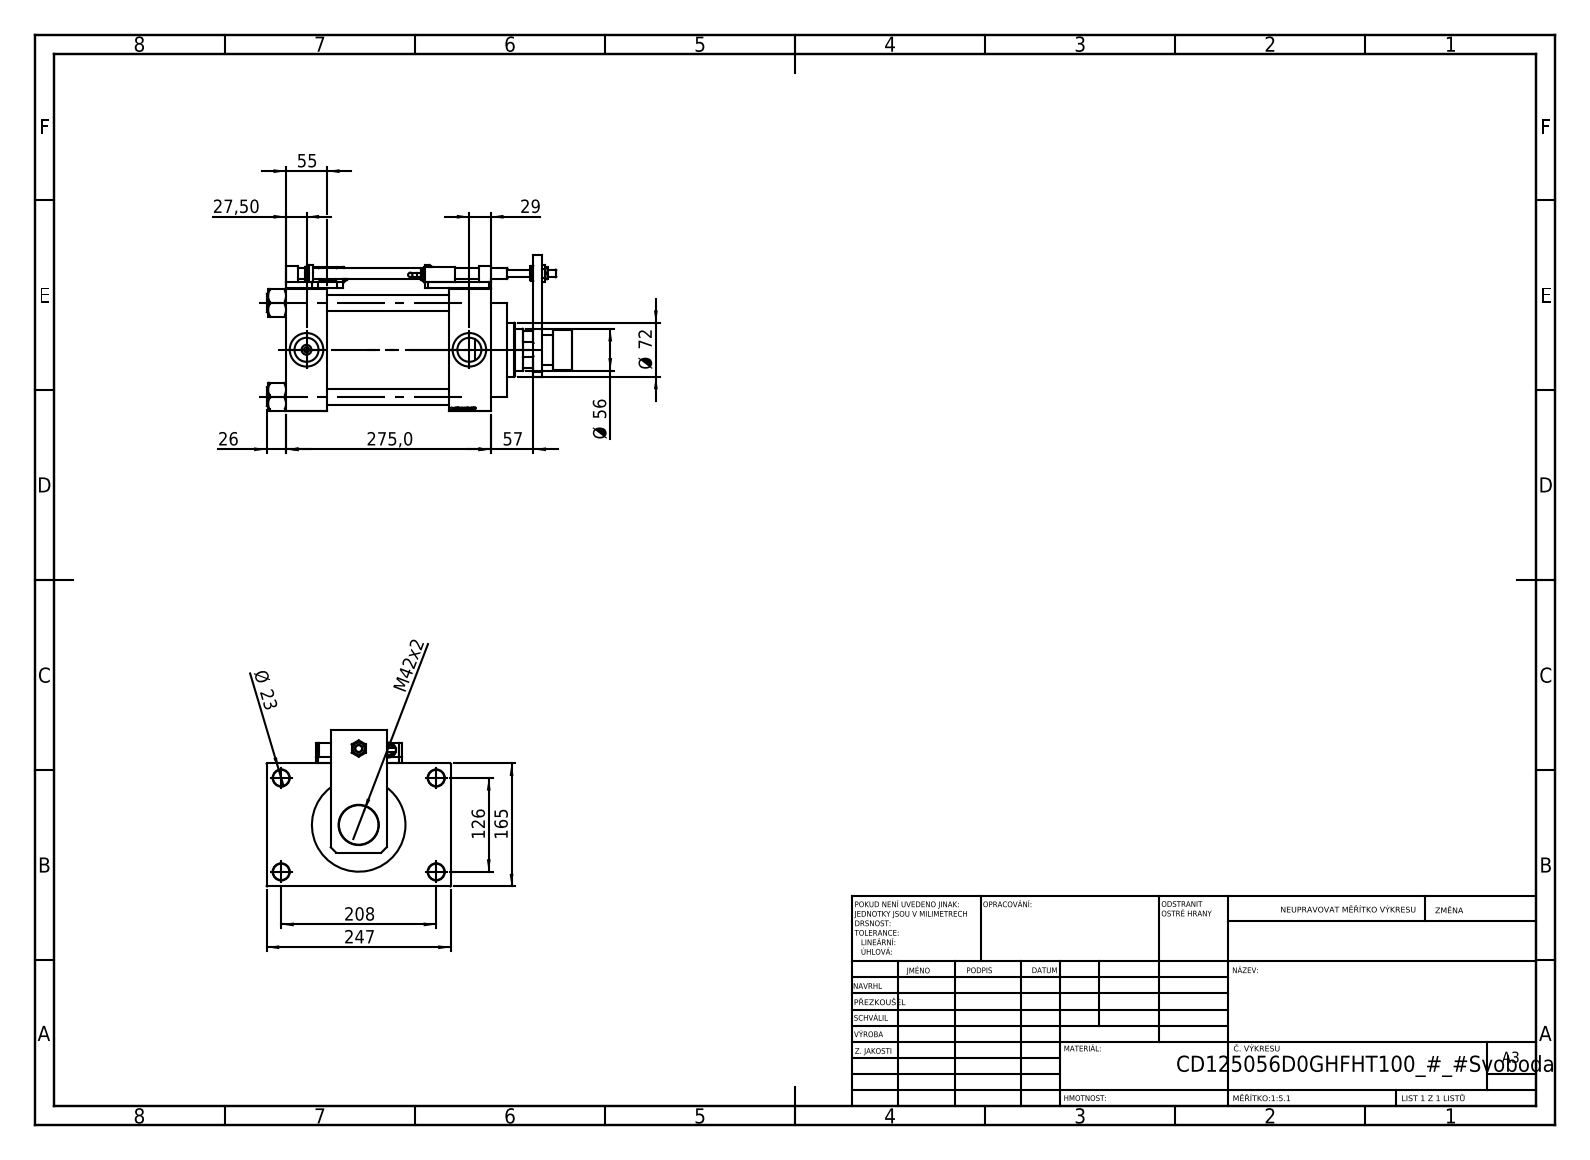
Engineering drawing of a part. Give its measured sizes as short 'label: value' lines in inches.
name: V215CD_SWITCH_Q_NUT; V215CD_SWITCH_Q_TYC; V215CD_SWITCH_Q_BLOK; V215CD_SWITCH_Q_DIMA (+7 more)
written by: SolidWorks 2019 (CONFIG_CONTROL_DESIGN)
unit: in
bodies: 25 solids, 1390 faces (669 planar, 158 cylindrical, 563 other)
size: 16.142 × 9.724 × 8.268
volume: 355 in³; area: 1 173 in²
holes: 8× ⌀0.866, 4× ⌀0.335, 4× ⌀0.531, 2× ⌀0.276, 2× ⌀1.269, 2× ⌀1.772, 1× ⌀0.394, 1× ⌀0.551, 1× ⌀1.594, 1× ⌀1.654, 1× ⌀2.205, 1× ⌀2.323
bosses: 4× ⌀0.984, 3× ⌀0.787, 2× ⌀0.63, 2× ⌀0.551, 2× ⌀0.236, 1× ⌀5.157, 1× ⌀2.835, 1× ⌀2.126
rounds: 4× R0.295
face distances: 6.496, 2.165, 8.622, 6.457, 10.827, 8.661, 2.205, 6.811, 0.315, 1.614
hole spacings: 1.616, 3.505, 4.787, 4.957, 5.215, 6.573, 8.233, 1.26
